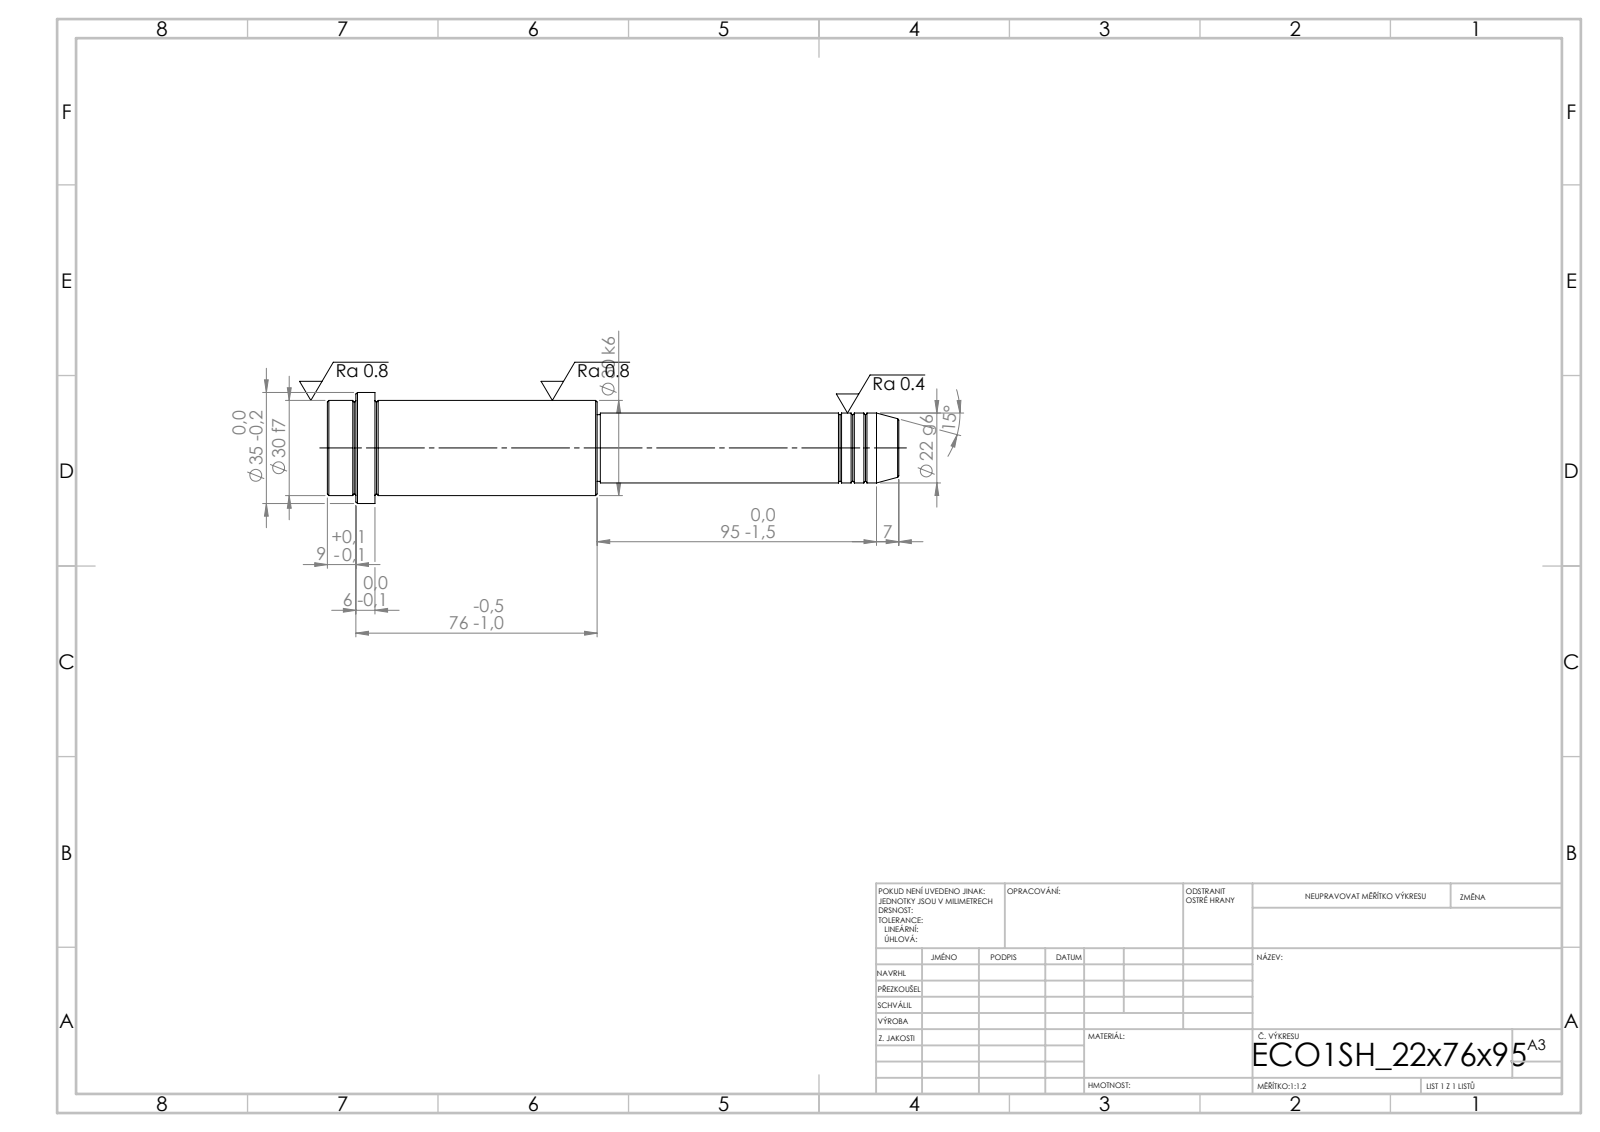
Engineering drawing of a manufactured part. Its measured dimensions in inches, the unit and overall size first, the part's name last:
Units: inches
Overall size (bounding box): 7.087 × 1.378 × 1.378
Round bosses / shafts (diameter × count): ⌀1.378 ×1, ⌀1.181 ×1, ⌀0.866 ×1, ⌀0.827 ×1
Main face-to-face distances: 3.346, 2.756, 0.591, 3.74, 6.496, 7.087, 6.732, 2.992, 0.236, 0.354
Volume: 5.924 in³ · Surface area: 25.78 in²
Bodies: 1 solid, 52 faces (6 planar, 16 cylindrical, 30 other)
STEP written by: SolidWorks 2019 (CONFIG_CONTROL_DESIGN)
